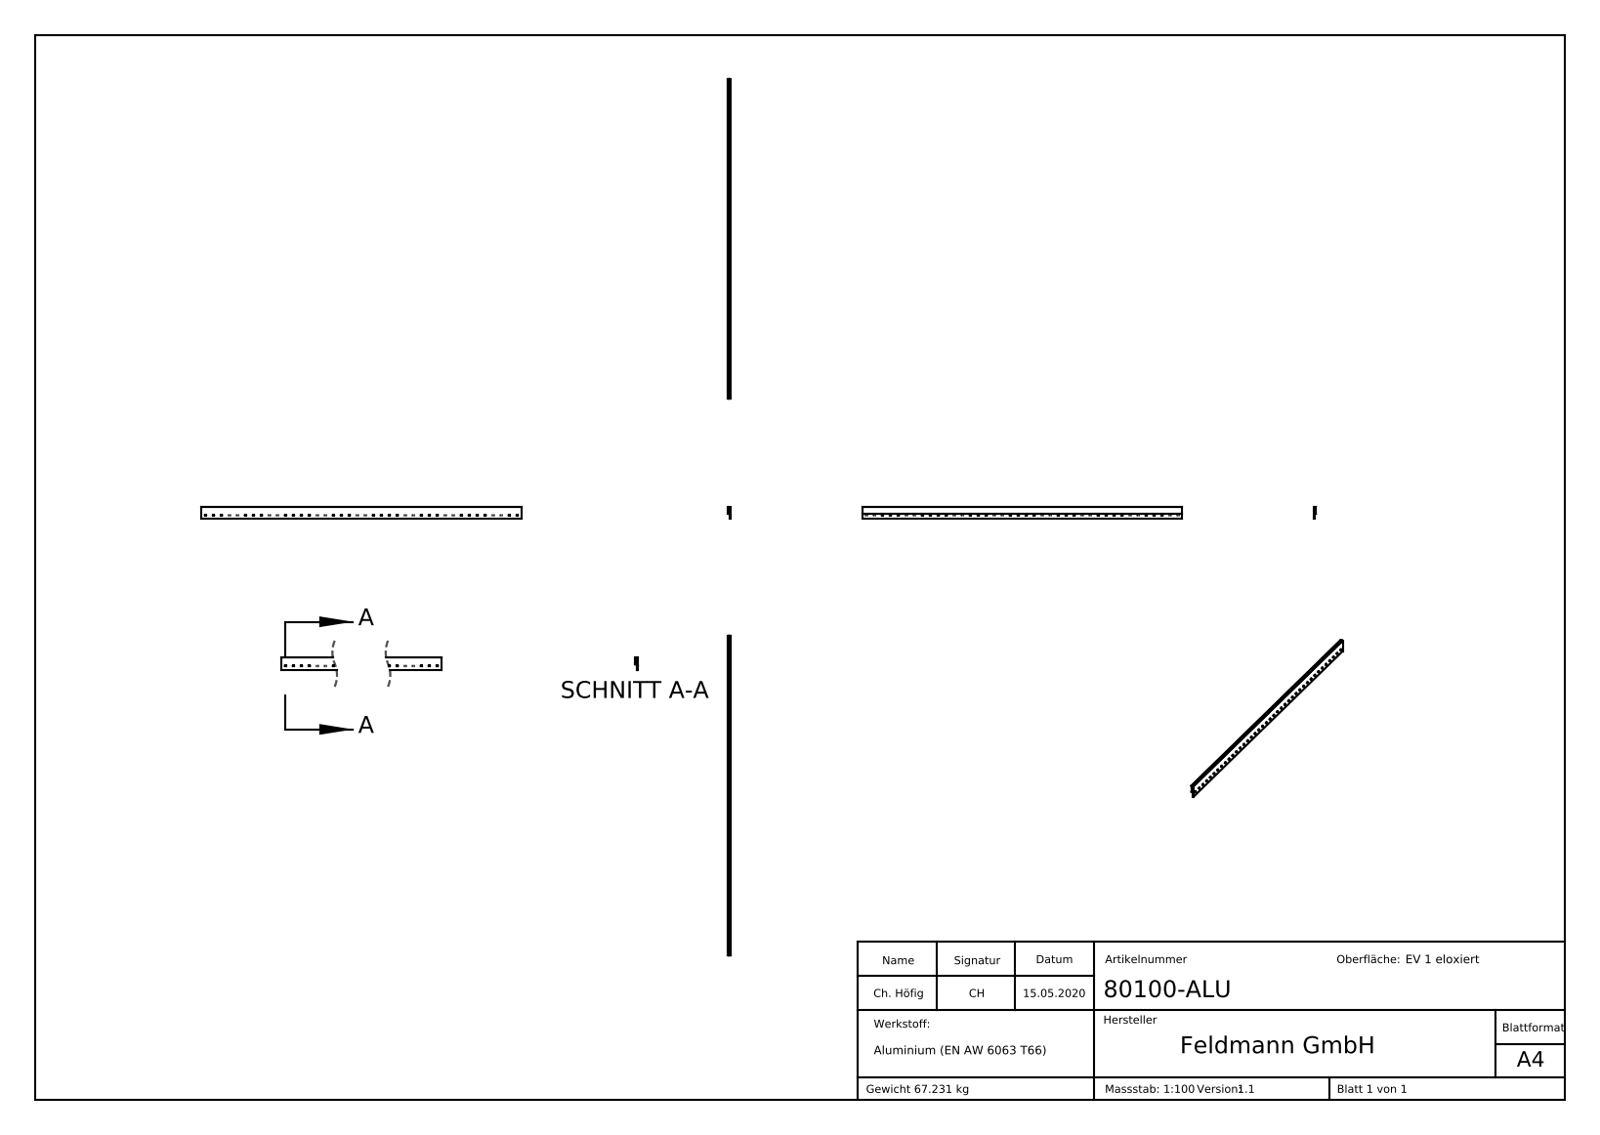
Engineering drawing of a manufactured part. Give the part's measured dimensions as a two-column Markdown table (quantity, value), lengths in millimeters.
| quantity | value |
| --- | --- |
| part name | 80100-ALU |
| STEP written by | SolidWorks 2015 (CONFIG_CONTROL_DESIGN) |
| units | millimeters |
| bodies | 1 solid, 412 faces (217 planar, 96 cylindrical, 99 other) |
| overall size | 6000 × 227.5 × 47 |
| volume | 24 900 000 mm³ |
| surface area | 4 721 000 mm² |
| partial cylindrical surfaces (radius × count) | 7 × 80, 0.5 × 9, 1 × 3, 0.65 × 2, 0.25 × 1 |
| main face-to-face distances | 12, 35, 47, 37.8, 9.2, 25.8, 2.8, 23, 122, 110 |
